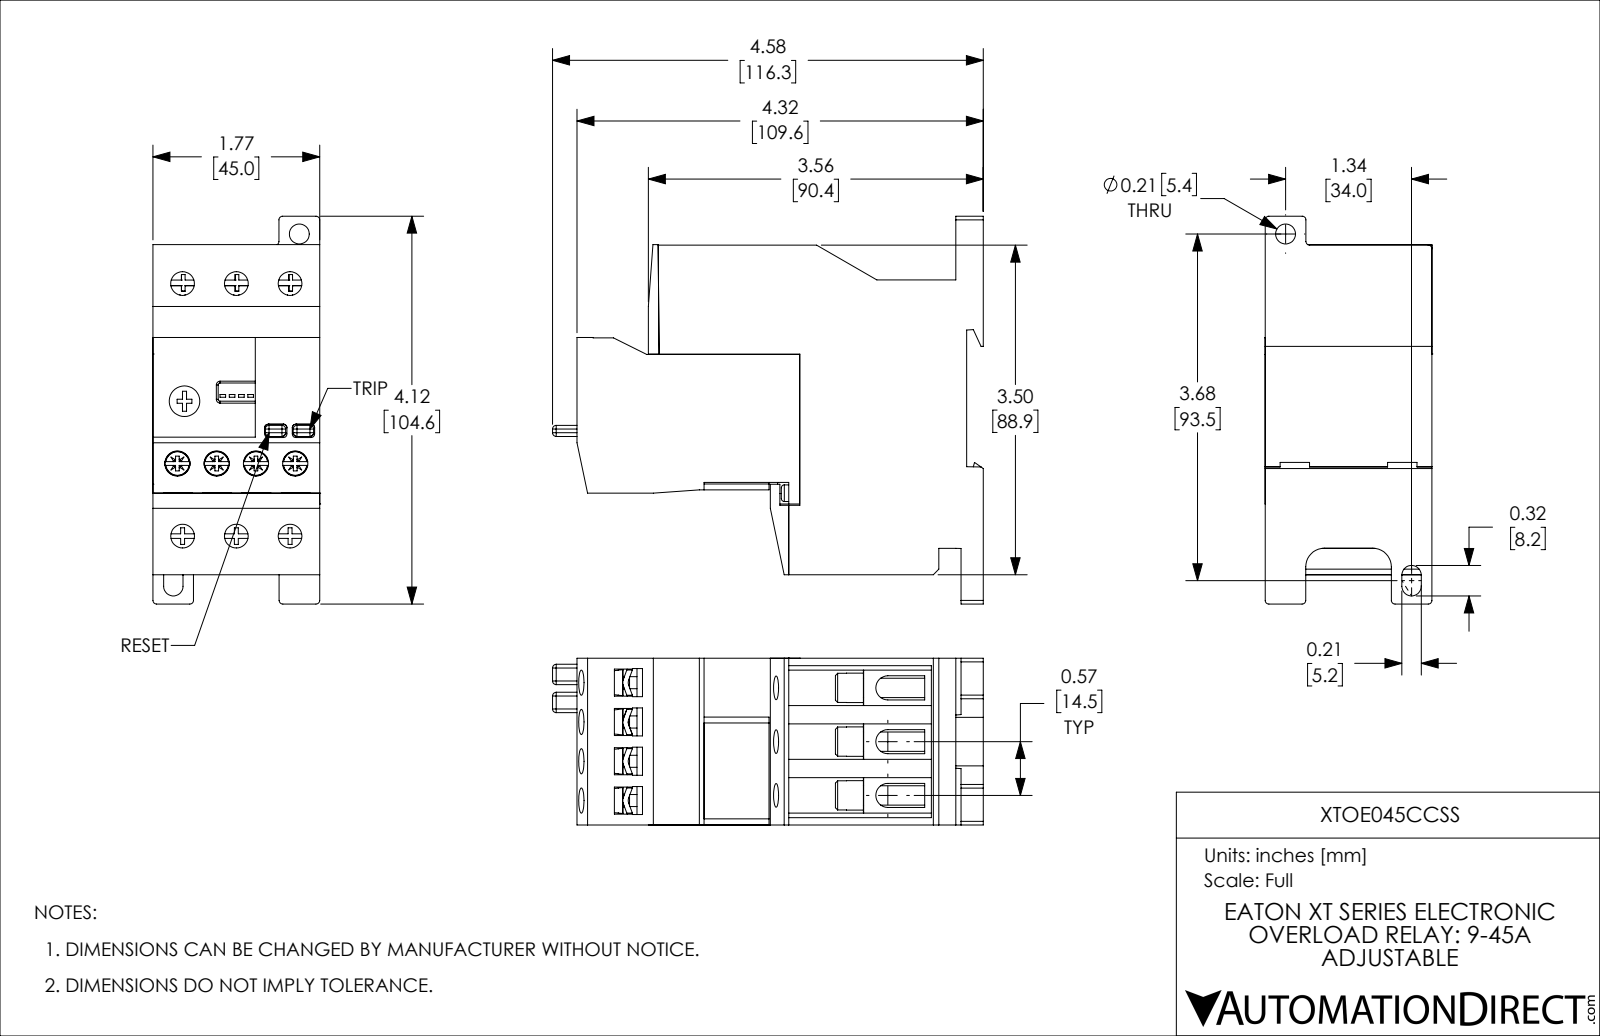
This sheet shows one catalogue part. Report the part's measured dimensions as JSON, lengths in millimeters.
{"part_name": "XTOE045CCSS", "step_written_by": "SolidWorks 2018 (AUTOMOTIVE_DESIGN)", "units": "millimeters", "bodies": {"solids": 42, "faces": 1296, "planar": 854, "cylindrical": 281, "other": 161}, "overall_size": [116.25, 104.6, 45.01], "volume_mm3": 292500, "surface_area_mm2": 75869, "round_holes": [[6.4, 6], [3.55, 5], [6.8, 4], [7.94, 3], [2.18, 2], [3.2, 2], [5.38, 1]], "round_bosses_or_shafts": [[3.4, 4], [3.25, 4], [2.8, 4], [2.5, 4], [8, 3], [4.5, 2], [8.27, 1]], "partial_cylinders_radius": [[0.5, 64], [0.3, 24], [1, 22], [2, 10], [3.25, 6], [0.8, 4], [0.4, 3], [1.57, 2]], "face_to_face_distances": [45, 14.5, 1.87, 10.89, 4.5, 45.01, 44.99, 29, 49.5, 16.37], "hole_center_spacings": [10.6, 21.2, 10.59, 10.61, 19.63, 48.55, 48.82, 51.07]}
